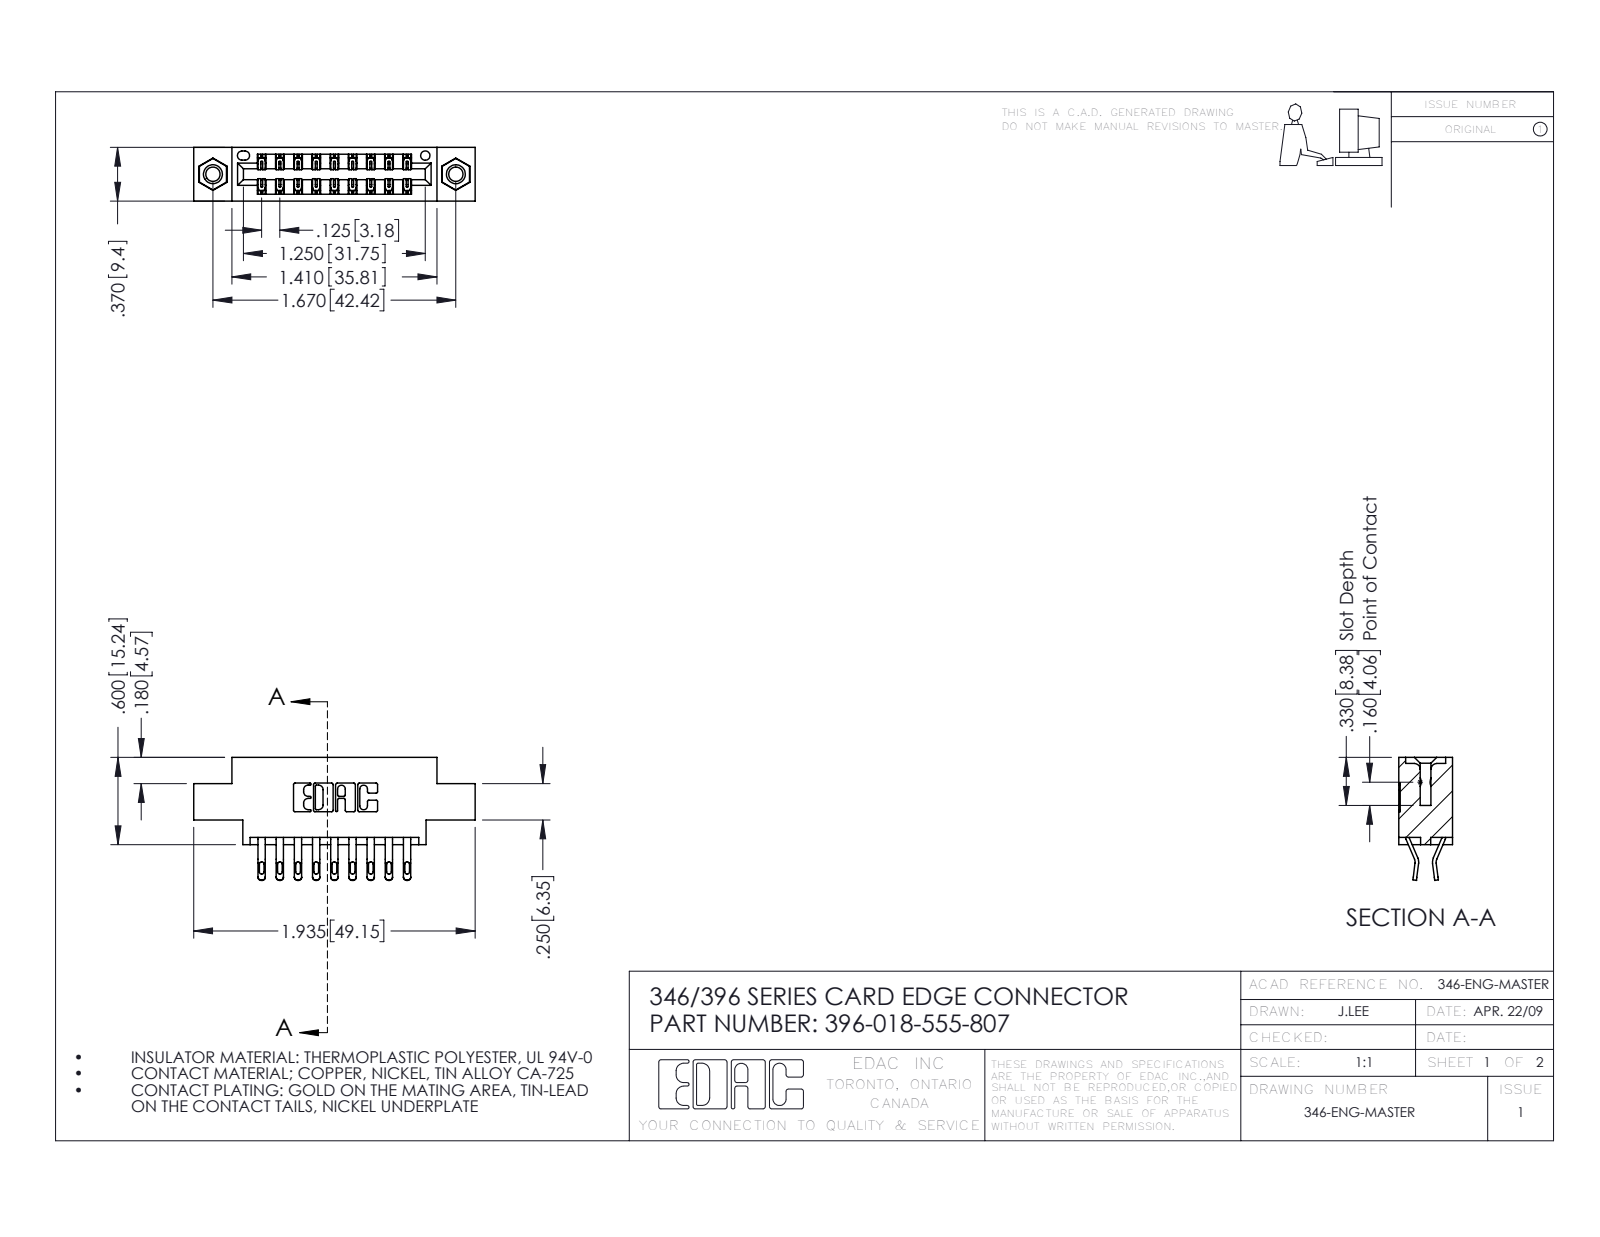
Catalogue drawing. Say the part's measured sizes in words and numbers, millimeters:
The part is named "345-250-001_345-250-005-103; 396-018-555-807; 346 Part_0.170 Offset - 0.156 Dia-TI; 345-292-001_555 Tail". Its 3-D file was written by "SolidWorks 2016 (CONFIG_CONTROL_DESIGN)". It is 21 solids with 1230 faces: 706 planar, 508 cylindrical and 16 other. Overall it measures 49.1 by 21.5 by 9.4 millimeters. Its volume is 4 420 cubic millimeters and its surface area 5 957 square millimeters. Round holes: 2 of diameter 2.5, 2 of diameter 3.2, 2 of diameter 4, 1 of diameter 1.6. Round bosses or shafts: 2 of diameter 3.9. Partial cylindrical surfaces (rounded edges, fillets, slot ends): 36 of radius 0.4, 36 of radius 0.5, 27 of radius 0.2, 22 of radius 0.3, 6 of radius 0.2, 6 of radius 0.8, 3 of radius 0.7, 2 of radius 0.3. The main face-to-face distances are 6.4, 9.4, 1.2, 8.2, 5.6, 3.8, 0.6, 1.8, 7.6, 2.5. The hole center spacings are 6.2, 37.2, 42.4.
